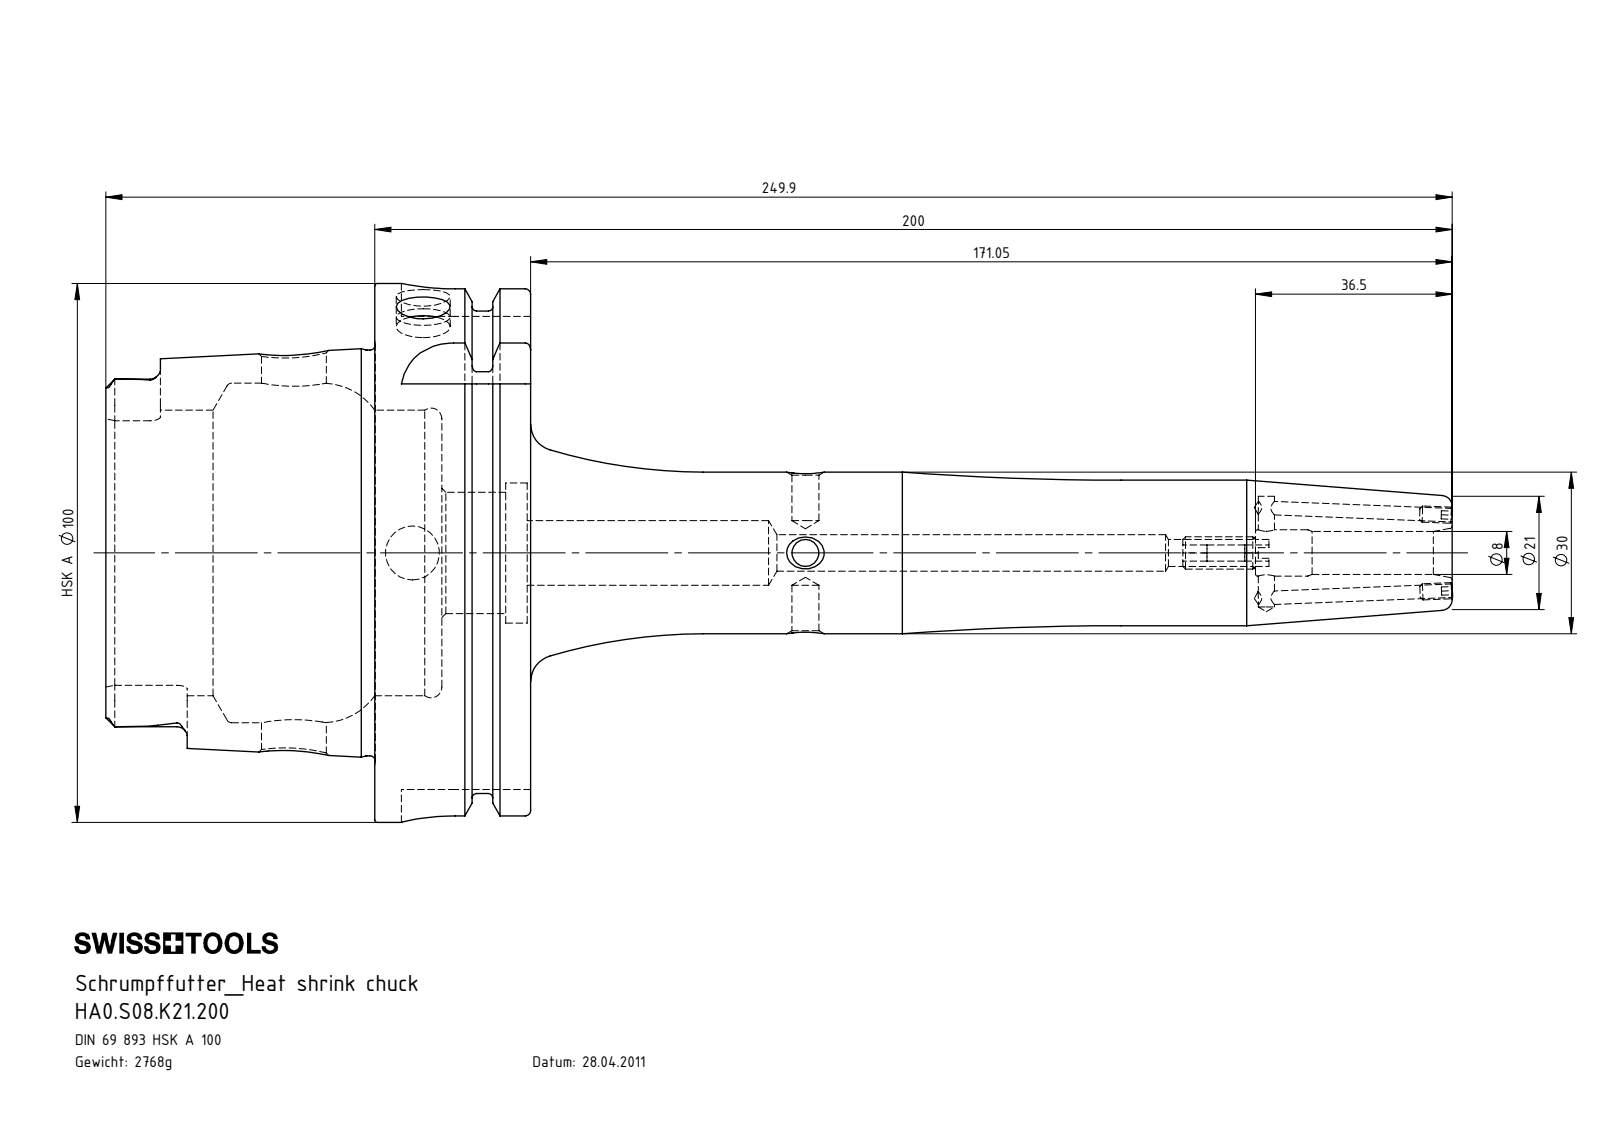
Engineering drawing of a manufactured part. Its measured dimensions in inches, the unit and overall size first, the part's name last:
Units: inches
Overall size (bounding box): 9.842 × 3.937 × 3.937
Round holes (diameter × count): ⌀0.197 ×3, ⌀0.394 ×3, ⌀0.098 ×2, ⌀0.118 ×2, ⌀0.472 ×2, ⌀0.268 ×1, ⌀0.315 ×1, ⌀0.339 ×1, ⌀0.886 ×1, ⌀1.024 ×1, ⌀2.087 ×1, ⌀2.48 ×1
Round bosses / shafts (diameter × count): ⌀0.118 ×2, ⌀3.937 ×1, ⌀3.62 ×1, ⌀2.963 ×1, ⌀1.181 ×1, ⌀1.063 ×1, ⌀0.236 ×1
Partial cylindrical surfaces — rounded edges, fillets, slot ends (radius × count): R0.075 ×6, R0.192 ×4, R0.394 ×4
Main face-to-face distances: 1.14, 0.49, 0.65, 1.965, 2.455, 3.104, 3.457, 3.079, 1.114, 0.624
Hole centre spacings: 2.872, 3.368, 3.738, 7.106
Volume: 21.51 in³ · Surface area: 109 in²
Bodies: 4 solids, 309 faces (95 planar, 90 cylindrical, 124 other)
Part name (STEP PRODUCT): HA0.S08.K21.200; ERU-CJ2.001.006; ERU-AN2.K01.016_A; HA0-S08.K21.200_C_Fertigbearbeitung
STEP written by: SolidWorks 2017 (CONFIG_CONTROL_DESIGN)
